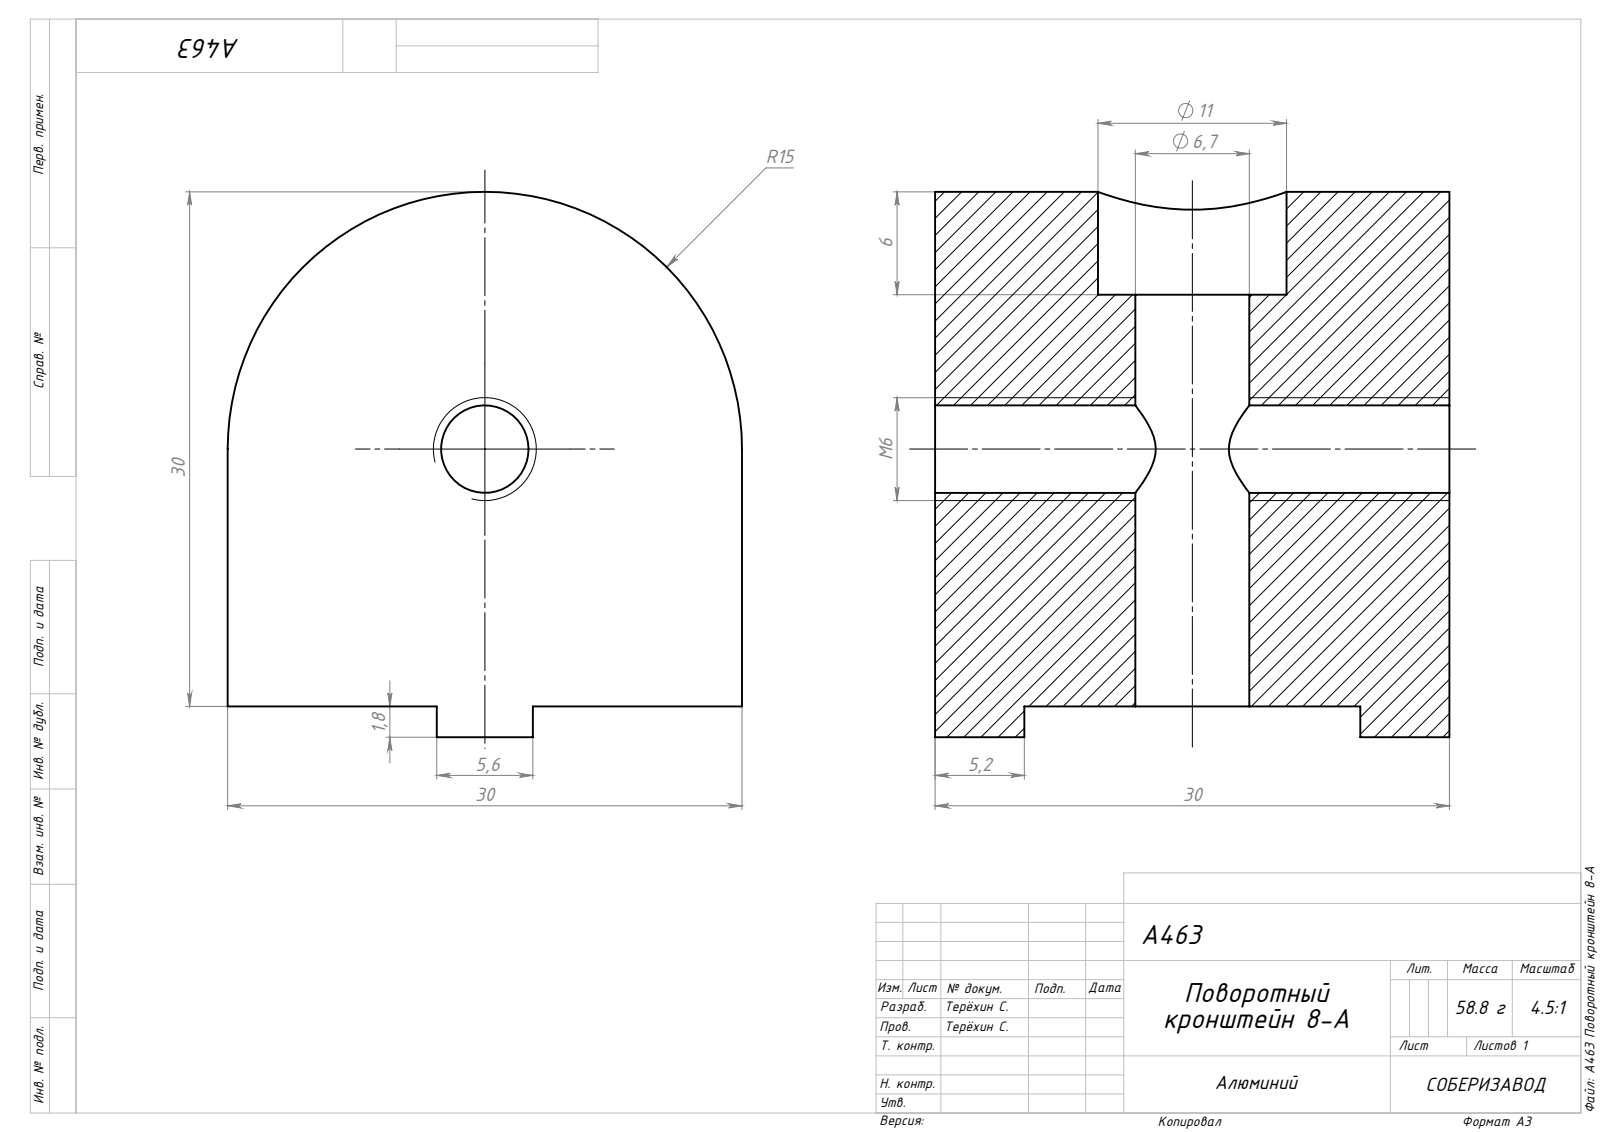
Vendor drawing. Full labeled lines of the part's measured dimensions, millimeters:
Part name (STEP PRODUCT): A463 Поворотный кронштейн 8-A
STEP written by: SolidWorks 2021 (AUTOMOTIVE_DESIGN)
Units: millimetres
Bodies: 1 solid, 24 faces (14 planar, 10 cylindrical, 0 other)
Overall size (bounding box): 31.8 × 30 × 30
Volume: 22 340 mm³ · Surface area: 5 824 mm²
Round holes (diameter × count): ⌀5.1 ×1, ⌀6.65 ×1, ⌀11 ×1
Partial cylindrical surfaces — rounded edges, fillets, slot ends (radius × count): R15 ×1
Main face-to-face distances: 30, 24, 1.8, 25.8, 12.2, 17.8, 5.2, 24.8, 5.6, 19.6
